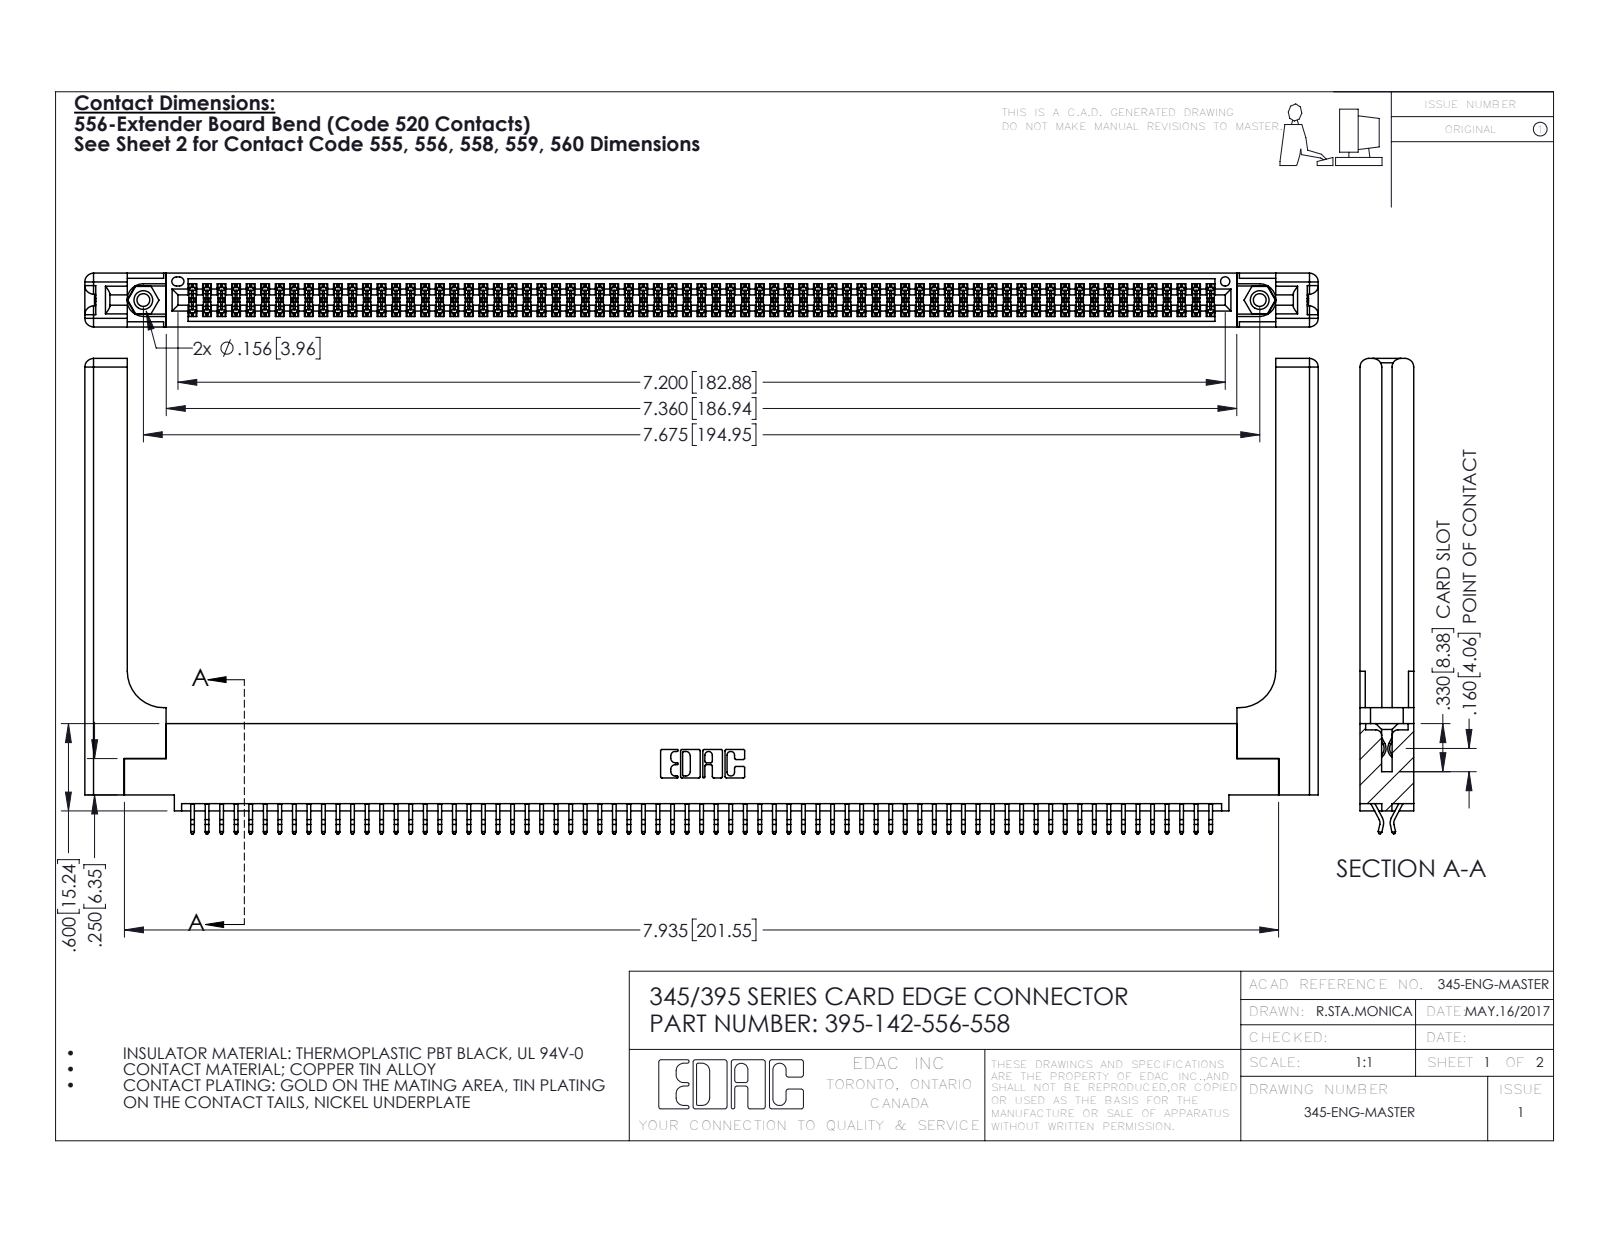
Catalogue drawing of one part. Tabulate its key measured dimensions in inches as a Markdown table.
| quantity | value |
| --- | --- |
| part name | 345 Part_0.110 Offset - 0.156 Dia-TH; 345-220-058_345-220-058; 345-250-001_345-250-001-102; 395-142-556-558 (+1 more) |
| STEP written by | SolidWorks 2016 (CONFIG_CONTROL_DESIGN) |
| units | inches |
| bodies | 147 solids, 8338 faces (5486 planar, 2792 cylindrical, 60 other) |
| overall size | 8.479 × 3.267 × 0.37 |
| volume | 1.805 in³ |
| surface area | 57.03 in² |
| round holes (diameter × count) | 0.089 × 2, 0.125 × 2, 0.156 × 2, 0.064 × 1 |
| round bosses / shafts (diameter × count) | 0.155 × 2 |
| partial cylindrical surfaces (radius × count) | 0.006 × 213, 0.01 × 22, 0.06 × 16, 0.007 × 6, 0.031 × 6, 0.026 × 3, 0.01 × 2, 0.014 × 2 |
| main face-to-face distances | 0.072, 0.298, 0.37, 0.025, 0.098, 0.272, 0.2, 0.225, 0.175, 0.148 |
| hole center spacings | 0.27, 7.439, 7.675 |
